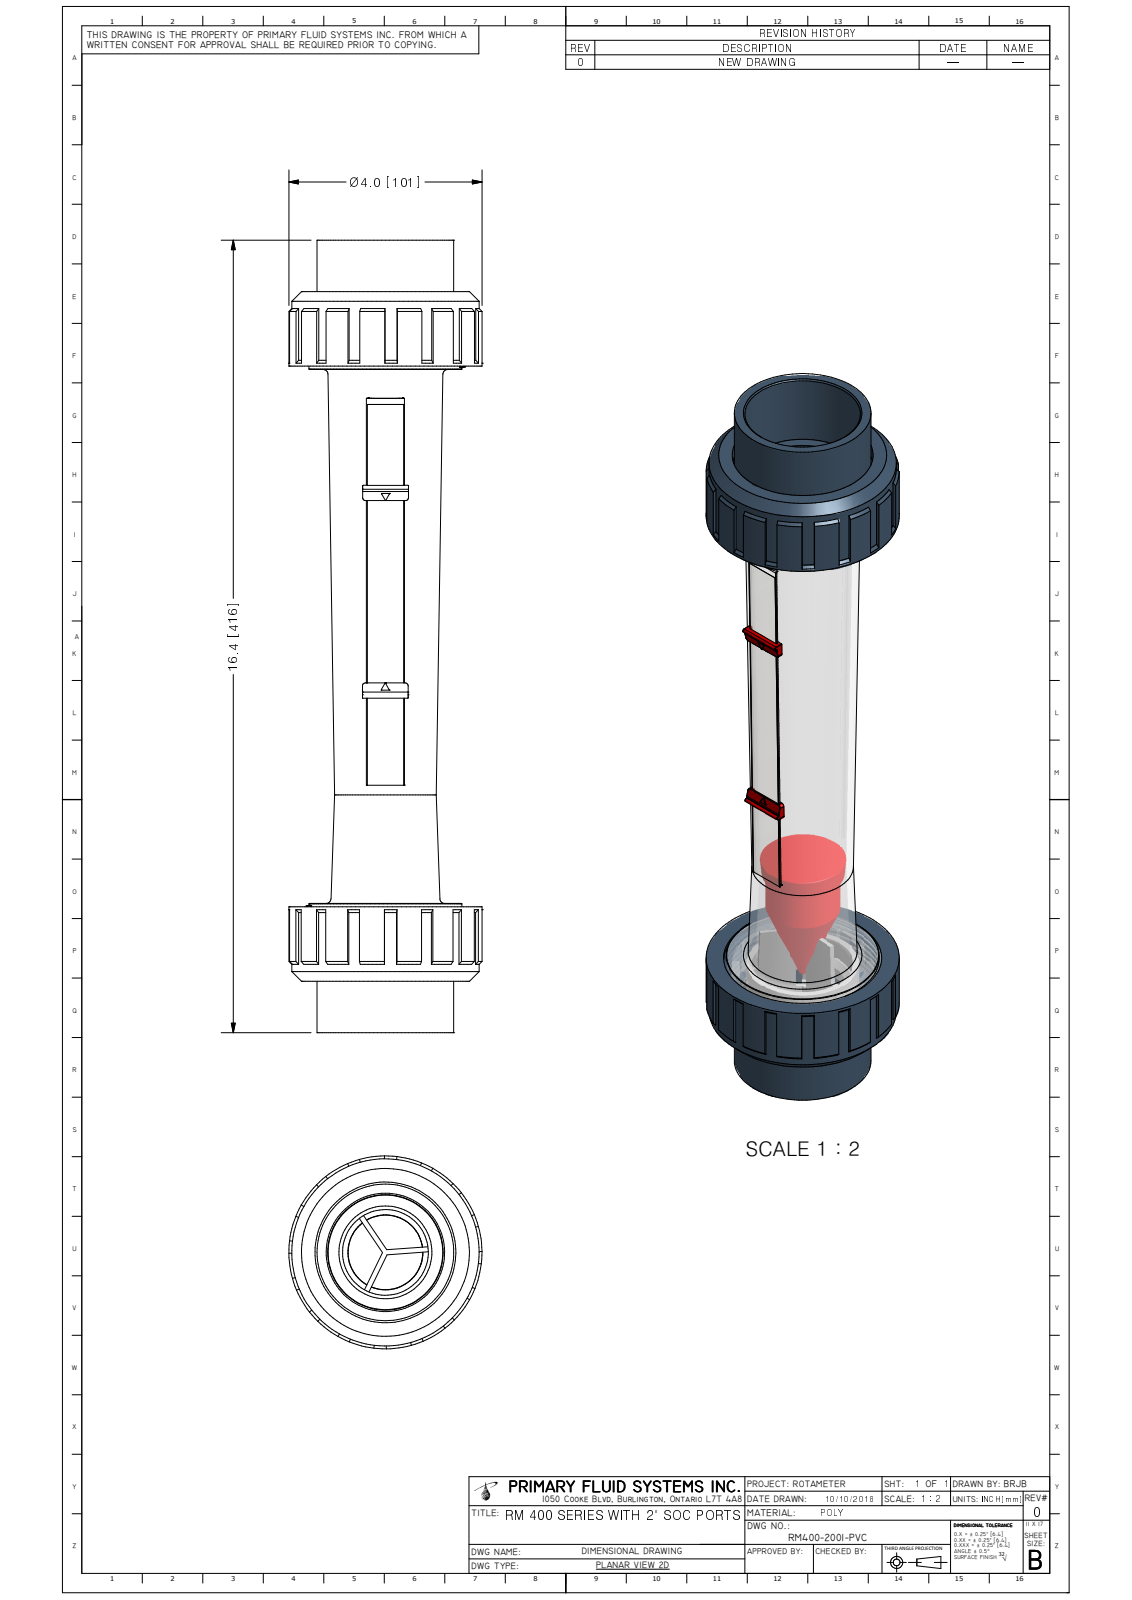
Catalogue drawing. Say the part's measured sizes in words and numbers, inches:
The part is named "RM400-200I-PVC_R0". Its 3-D file was written by "Autodesk Inventor 2009 (AUTOMOTIVE_DESIGN)". It is 1 solid with 550 faces: 185 planar, 109 cylindrical and 256 other. Overall it measures 16.388 by 3.99 by 3.99 inches. Its volume is 78.5 cubic inches and its surface area 285.7 square inches. Round holes: 1 of diameter 2.91, 1 of diameter 3.147, 1 of diameter 3.265, 1 of diameter 3.265. Round bosses or shafts: 1 of diameter 3.99, 1 of diameter 3.87, 1 of diameter 3.158, 1 of diameter 3.062, 1 of diameter 2.824. Partial cylindrical surfaces (rounded edges, fillets, slot ends): 18 of radius 0.008, 16 of radius 0.01, 9 of radius 0.004, 8 of radius 0.006, 4 of radius 0.06, 2 of radius 0.008, 2 of radius 0.04, 2 of radius 0.75. The main face-to-face distances are 1.105, 12.283, 0.435, 1.54, 12.718, 13.823, 1.174, 12.214, 0.069, 11.109.
